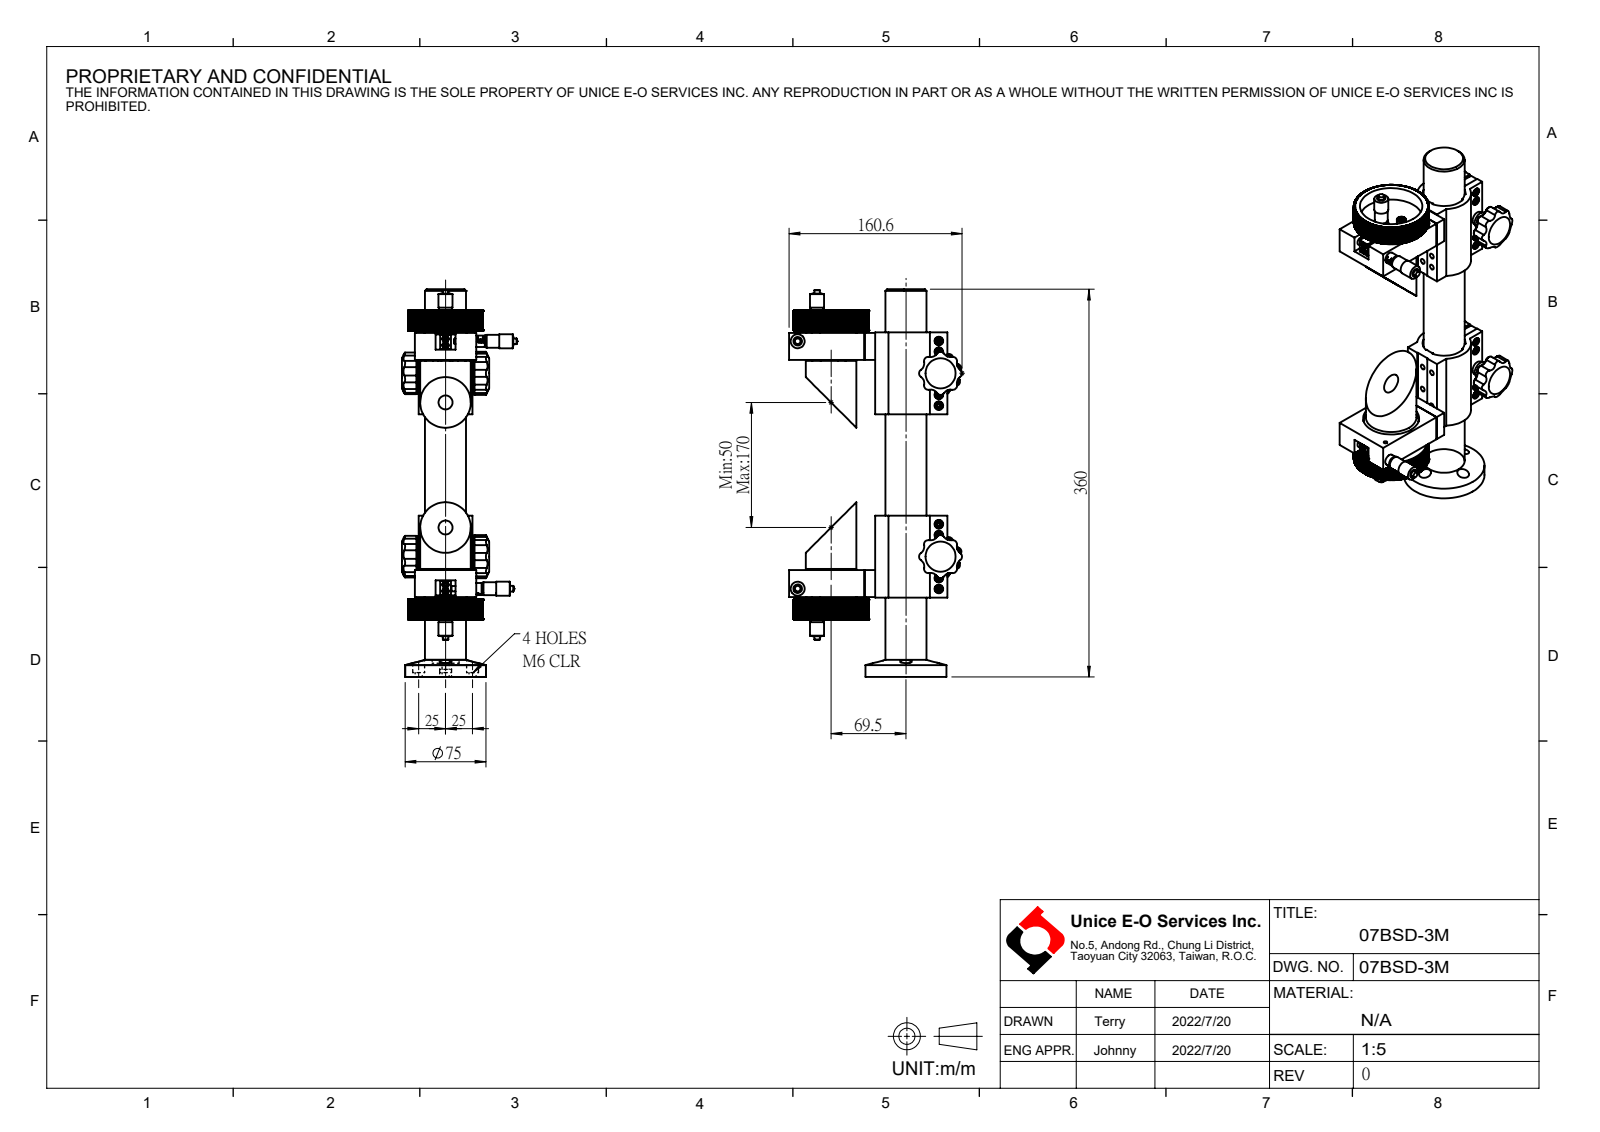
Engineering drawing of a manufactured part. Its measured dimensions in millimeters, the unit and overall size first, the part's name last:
Units: millimetres
Overall size (bounding box): 359.7 × 160.6 × 106.9
Round holes (diameter × count): ⌀5 ×22, ⌀3.3 ×17, ⌀8 ×14, ⌀4.5 ×12, ⌀2.5 ×9, ⌀6.6 ×9, ⌀11 ×9, ⌀3 ×5, ⌀3.4 ×4, ⌀6 ×4, ⌀4.2 ×3, ⌀10.6 ×3
Round bosses / shafts (diameter × count): ⌀4 ×15, ⌀7 ×12, ⌀3 ×12, ⌀5.5 ×7, ⌀13 ×3, ⌀12 ×3, ⌀10.5 ×3, ⌀9.9 ×3
Partial cylindrical surfaces — rounded edges, fillets, slot ends (radius × count): R4 ×32, R7 ×32, R2 ×2, R2.5 ×2, R20 ×1, R25 ×1, R34.75 ×1, R48 ×1
Main face-to-face distances: 3, 10, 24, 27, 228, 2, 6, 6.5, 30, 225
Hole centre spacings: 170, 25, 12.5, 27.95, 50, 17.68, 51.54, 170.46
Volume: 1 106 000 mm³ · Surface area: 309 862 mm²
Bodies: 90 solids, 4655 faces (2157 planar, 1152 cylindrical, 1346 other)
Part name (STEP PRODUCT): 07BSD-3M
STEP written by: SolidWorks 2021 (CONFIG_CONTROL_DESIGN)
